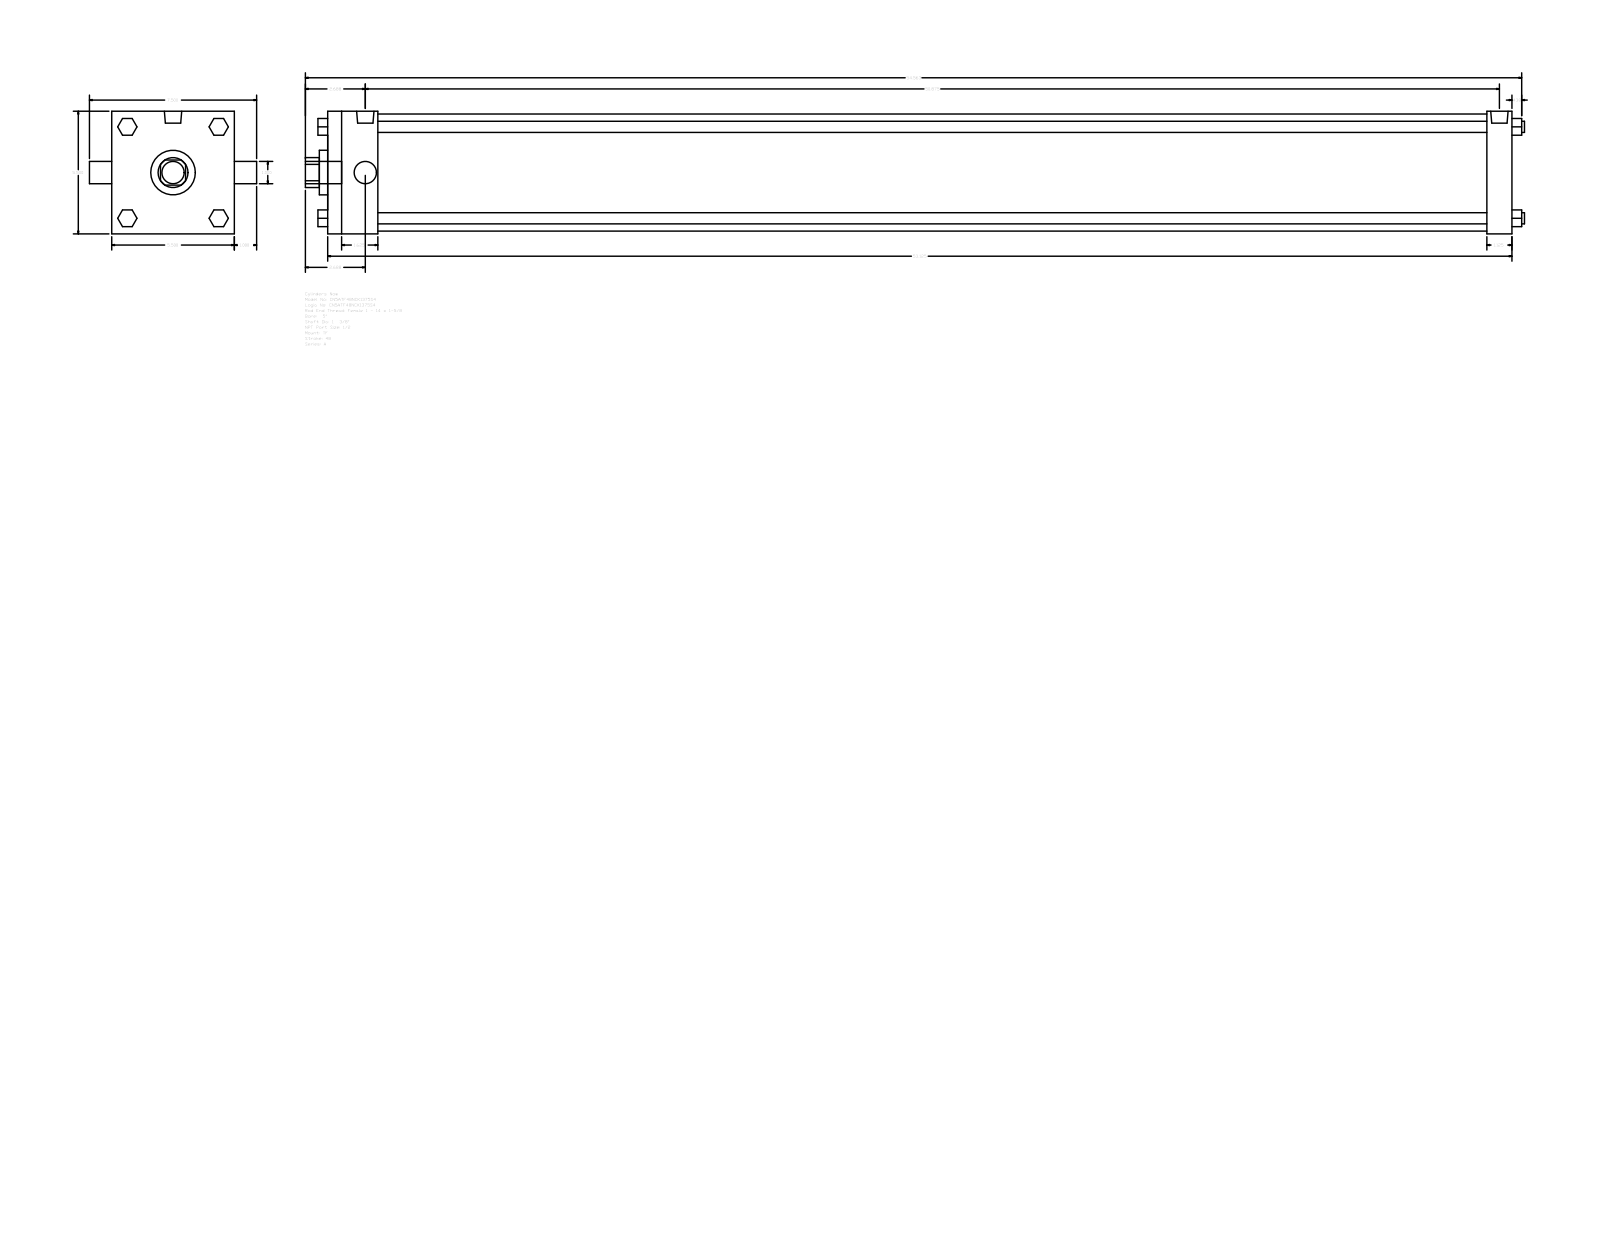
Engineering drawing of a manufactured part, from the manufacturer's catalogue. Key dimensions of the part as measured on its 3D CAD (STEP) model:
Part name (STEP PRODUCT): A_TF__0500_1.375
STEP written by: GSSL Pune (CONFIG_CONTROL_DESIGN)
Units: millimetres
Bodies: 0 solids, 120 faces (92 planar, 28 cylindrical, 0 other)
Overall size (bounding box): 1389.06 × 190.5 × 139.7
Round holes (diameter × count): ⌀25.4 ×1, ⌀34.92 ×1, ⌀50.8 ×1, ⌀133.35 ×1
Round bosses / shafts (diameter × count): ⌀12.7 ×4, ⌀8.73 ×3, ⌀19.77 ×2, ⌀25.4 ×1
Partial cylindrical surfaces — rounded edges, fillets, slot ends (radius × count): R17.06 ×1
Main face-to-face distances: 139.7, 1349.38, 28.58, 1320.8, 57.15, 1263.65, 1292.23, 19.05, 52.07, 90.18
